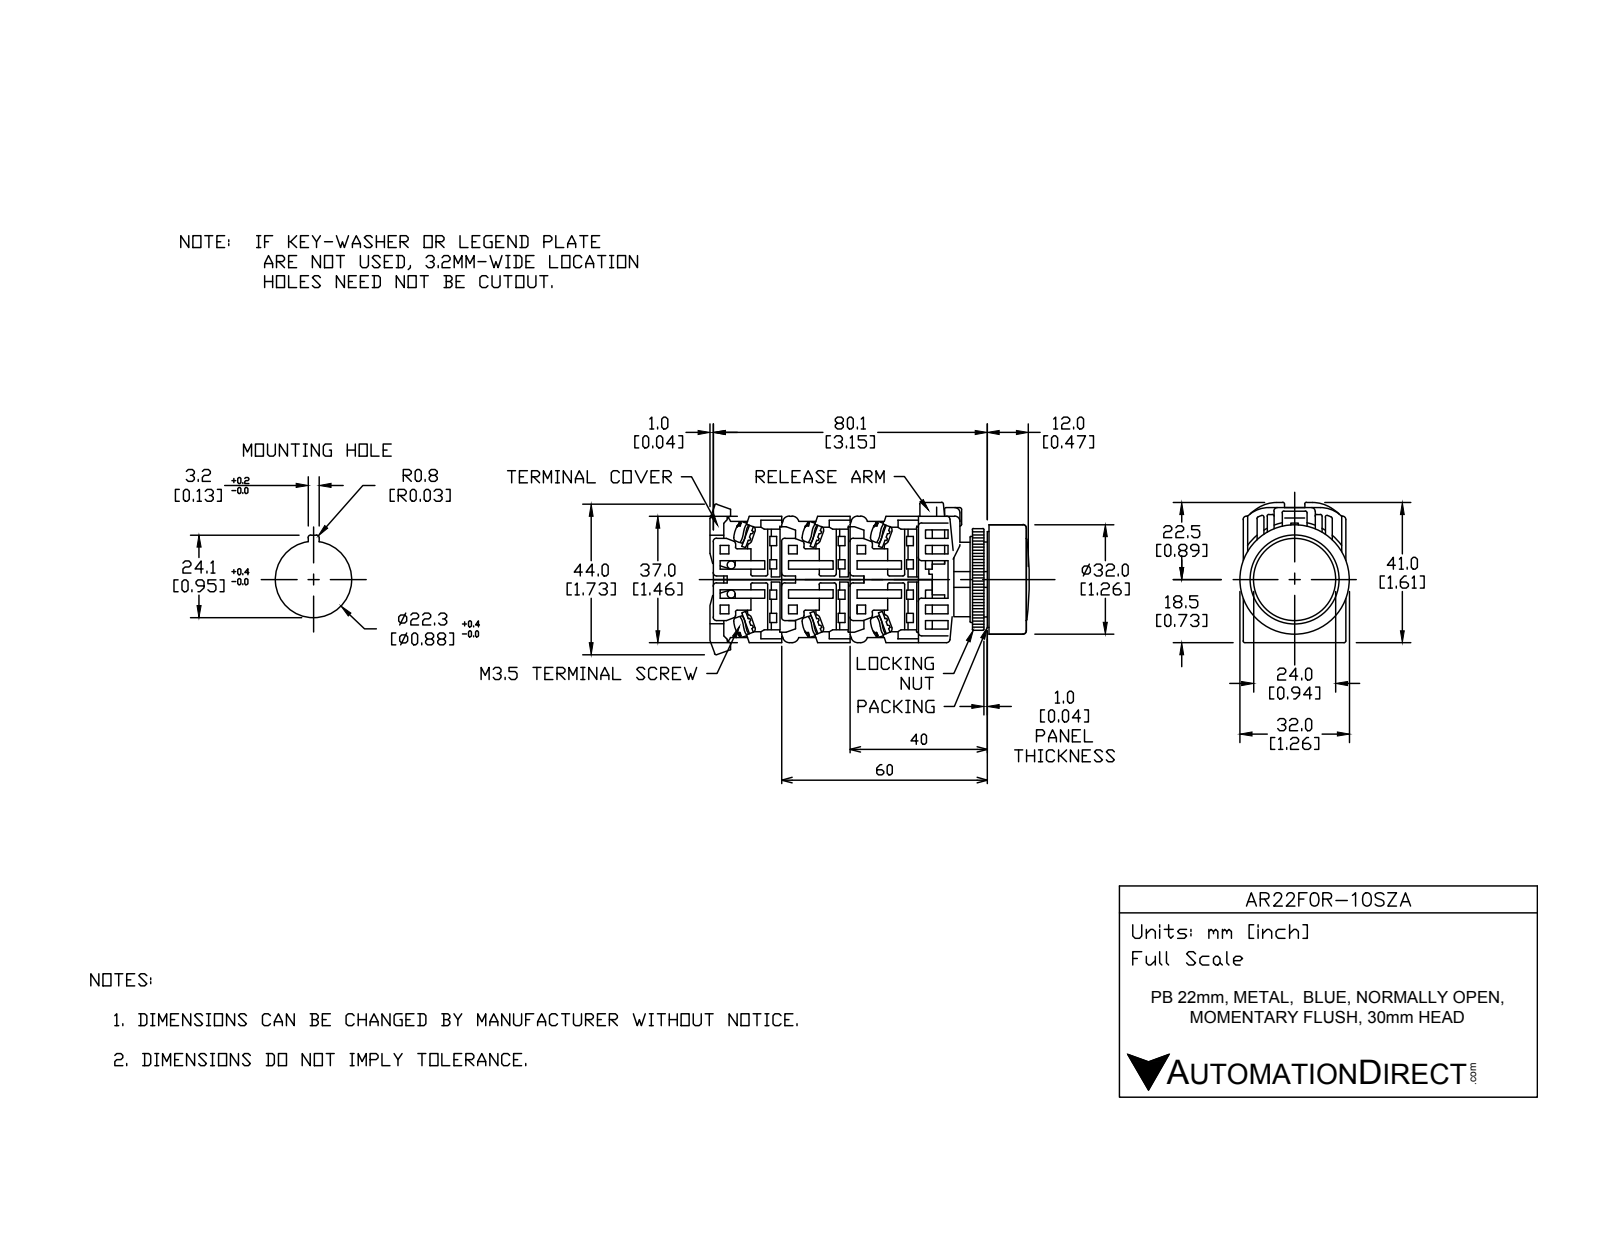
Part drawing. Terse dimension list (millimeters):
name: AR22F0R-10SZA
written by: SolidWorks 2017 (AUTOMOTIVE_DESIGN)
unit: mm
bodies: 12 solids, 295 faces (201 planar, 74 cylindrical, 20 other)
size: 52.75 × 41 × 32
volume: 27 343 mm³; area: 19 391 mm²
holes: 1× ⌀21.8, 1× ⌀22, 1× ⌀25, 1× ⌀31
bosses: 2× ⌀5, 1× ⌀32, 1× ⌀30.5, 1× ⌀29.8, 1× ⌀24, 1× ⌀23.8, 1× ⌀21.75, 1× ⌀17
rounds: 23× R0.5, 4× R1.75, 4× R5, 2× R4, 1× R16.59, 1× R17.59
face distances: 1, 28.5, 18, 3, 2, 29, 30, 10.5, 8, 20.5
